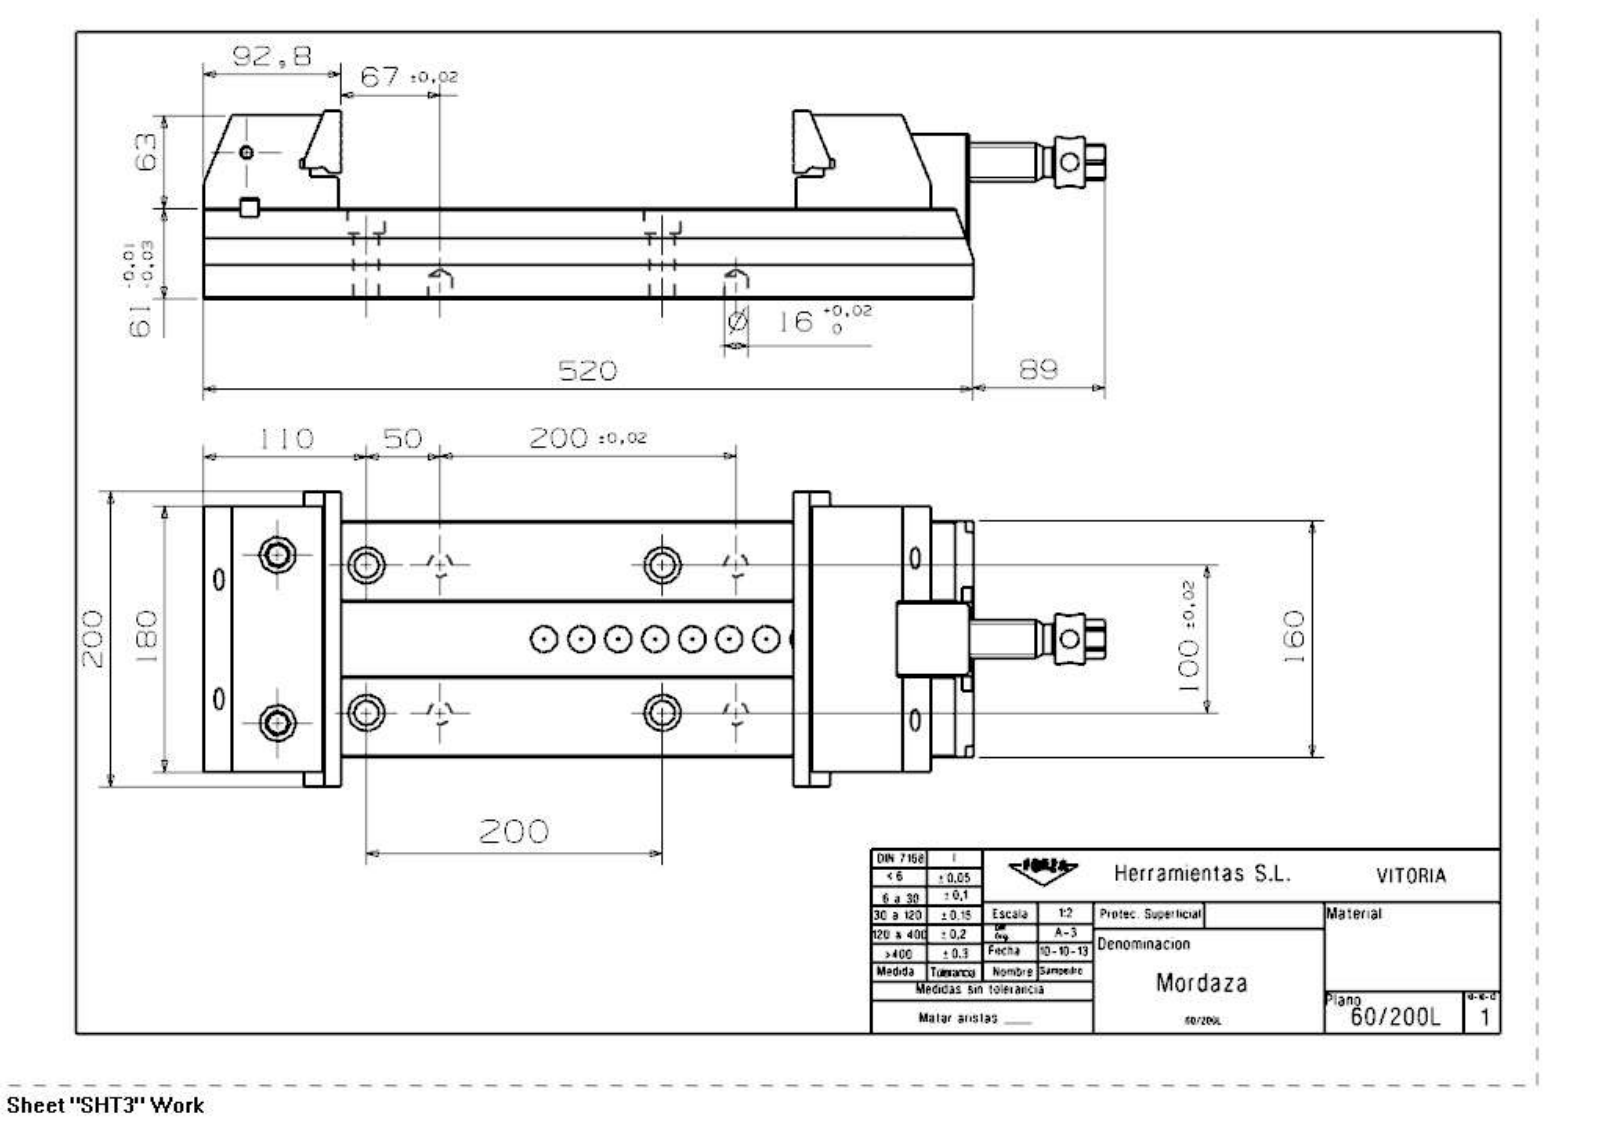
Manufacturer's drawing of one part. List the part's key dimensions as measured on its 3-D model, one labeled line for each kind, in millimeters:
Part name (STEP PRODUCT): 15090 Montaje taco atras; 60_200L_Mordaza
STEP written by: SIEMENS PLM Software NX 7.5 (CONFIG_CONTROL_DESIGN)
Units: millimetres
Bodies: 12 solids, 478 faces (280 planar, 132 cylindrical, 66 other)
Overall size (bounding box): 609 × 200 × 126.95
Volume: 5 833 000 mm³ · Surface area: 633 061 mm²
Round holes (diameter × count): ⌀15 ×6, ⌀17 ×6, ⌀25 ×6, ⌀16 ×5, ⌀6.99 ×4, ⌀8.5 ×4, ⌀10 ×4, ⌀8.78 ×3, ⌀10.58 ×3, ⌀13 ×3, ⌀19 ×3, ⌀12 ×2
Round bosses / shafts (diameter × count): ⌀34 ×1, ⌀33.8 ×1, ⌀26 ×1, ⌀20 ×1, ⌀16.5 ×1
Partial cylindrical surfaces — rounded edges, fillets, slot ends (radius × count): R0.4 ×24, R20 ×4, R1.6 ×2, R6 ×2, R7 ×2, R4 ×1, R9 ×1, R10.5 ×1
Main face-to-face distances: 61, 63, 28.9, 32.1, 27.8, 160, 45, 124, 95.1, 10
Hole centre spacings: 14.5, 95.5, 50, 81, 100, 110, 111.8, 200
